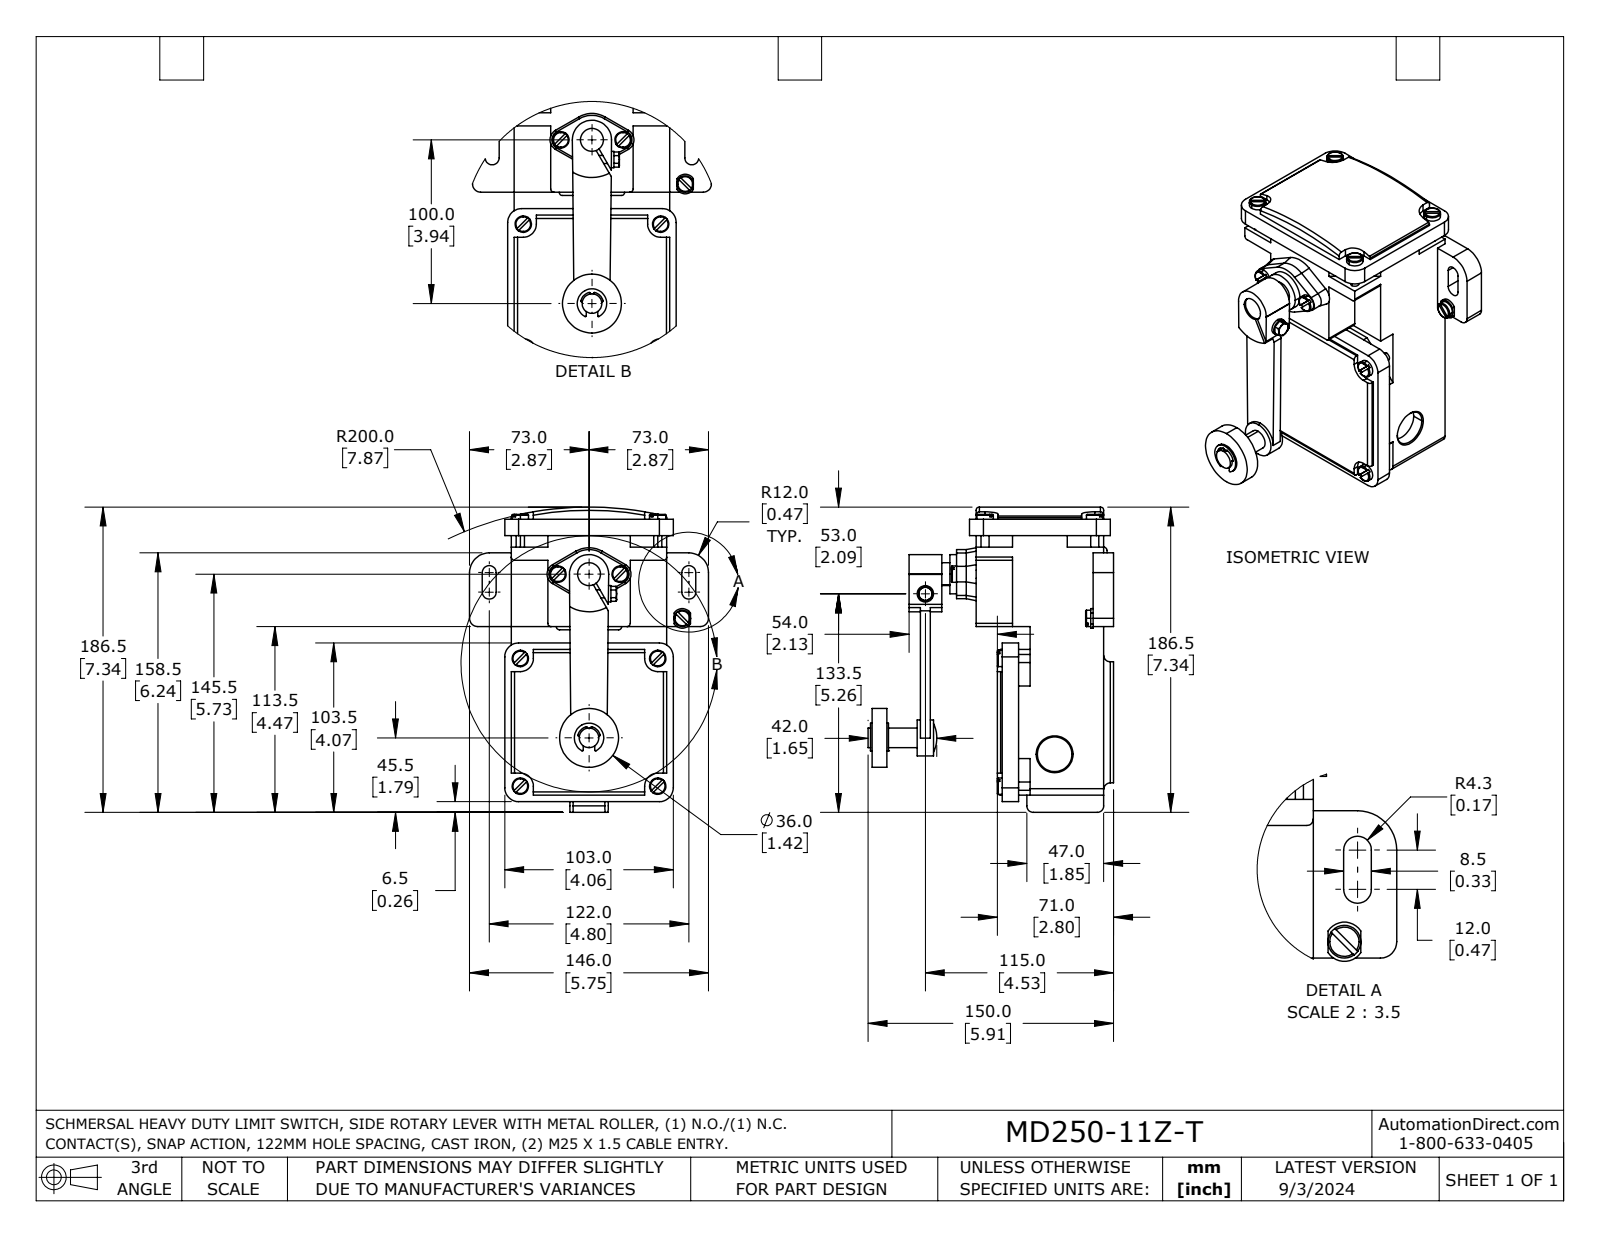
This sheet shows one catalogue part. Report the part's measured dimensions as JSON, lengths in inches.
{"part_name": "MD 250-11Z-T", "step_written_by": "SolidWorks 2023 (AUTOMOTIVE_DESIGN)", "units": "inches", "bodies": {"solids": 1, "faces": 421, "planar": 207, "cylindrical": 138, "other": 76}, "overall_size": [7.343, 5.906, 5.748], "volume_in3": 74.88, "surface_area_in2": 172.6, "round_holes": [[0.163, 1], [0.197, 1], [0.551, 1], [0.833, 1]], "round_bosses_or_shafts": [[0.394, 12], [0.197, 8], [2.913, 1], [1.417, 1], [0.945, 1], [0.866, 1], [0.709, 1], [0.472, 1]], "partial_cylinders_radius": [[0.079, 10], [0.315, 8], [0.335, 8], [0.02, 6], [0.157, 4], [0.167, 4], [0.039, 2], [0.197, 2]], "face_to_face_distances": [0.236, 2.559, 3.74, 2.795, 0.512, 0.157, 0.394, 0.276, 0.669, 0.787], "hole_center_spacings": [4.956]}
